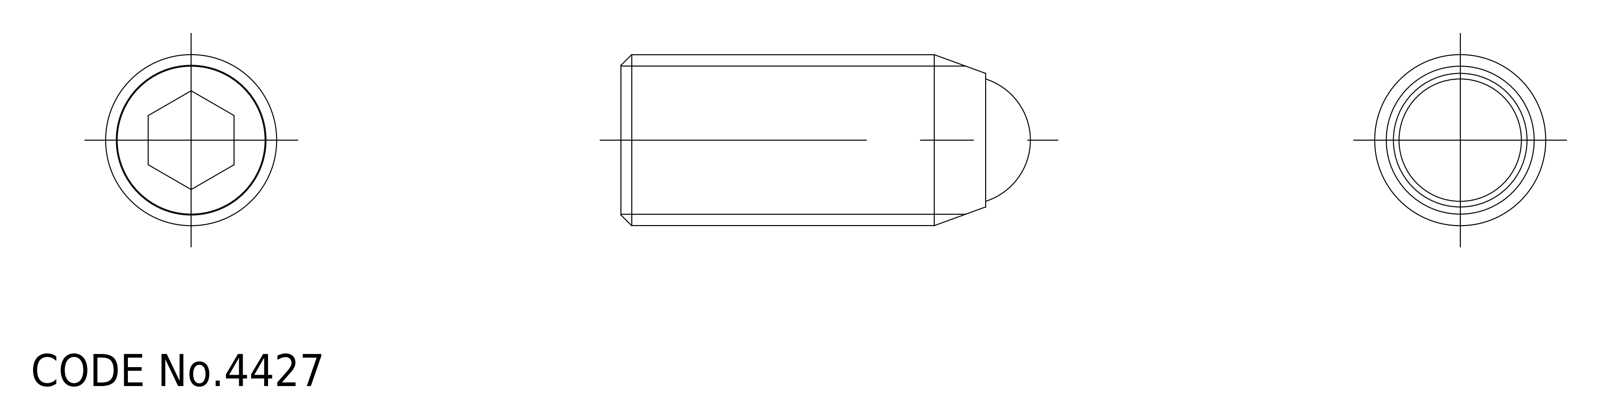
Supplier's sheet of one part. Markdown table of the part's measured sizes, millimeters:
| quantity | value |
| --- | --- |
| part name | ball; SCSS_M16_35_R_18570_36 |
| STEP written by | CADfix (AUTOMOTIVE_DESIGN) |
| units | millimeters |
| bodies | 2 solids, 20 faces (0 planar, 0 cylindrical, 20 other) |
| overall size | 38.3 × 16 × 16 |
| volume | 5 907 mm³ |
| surface area | 3 106 mm² |
